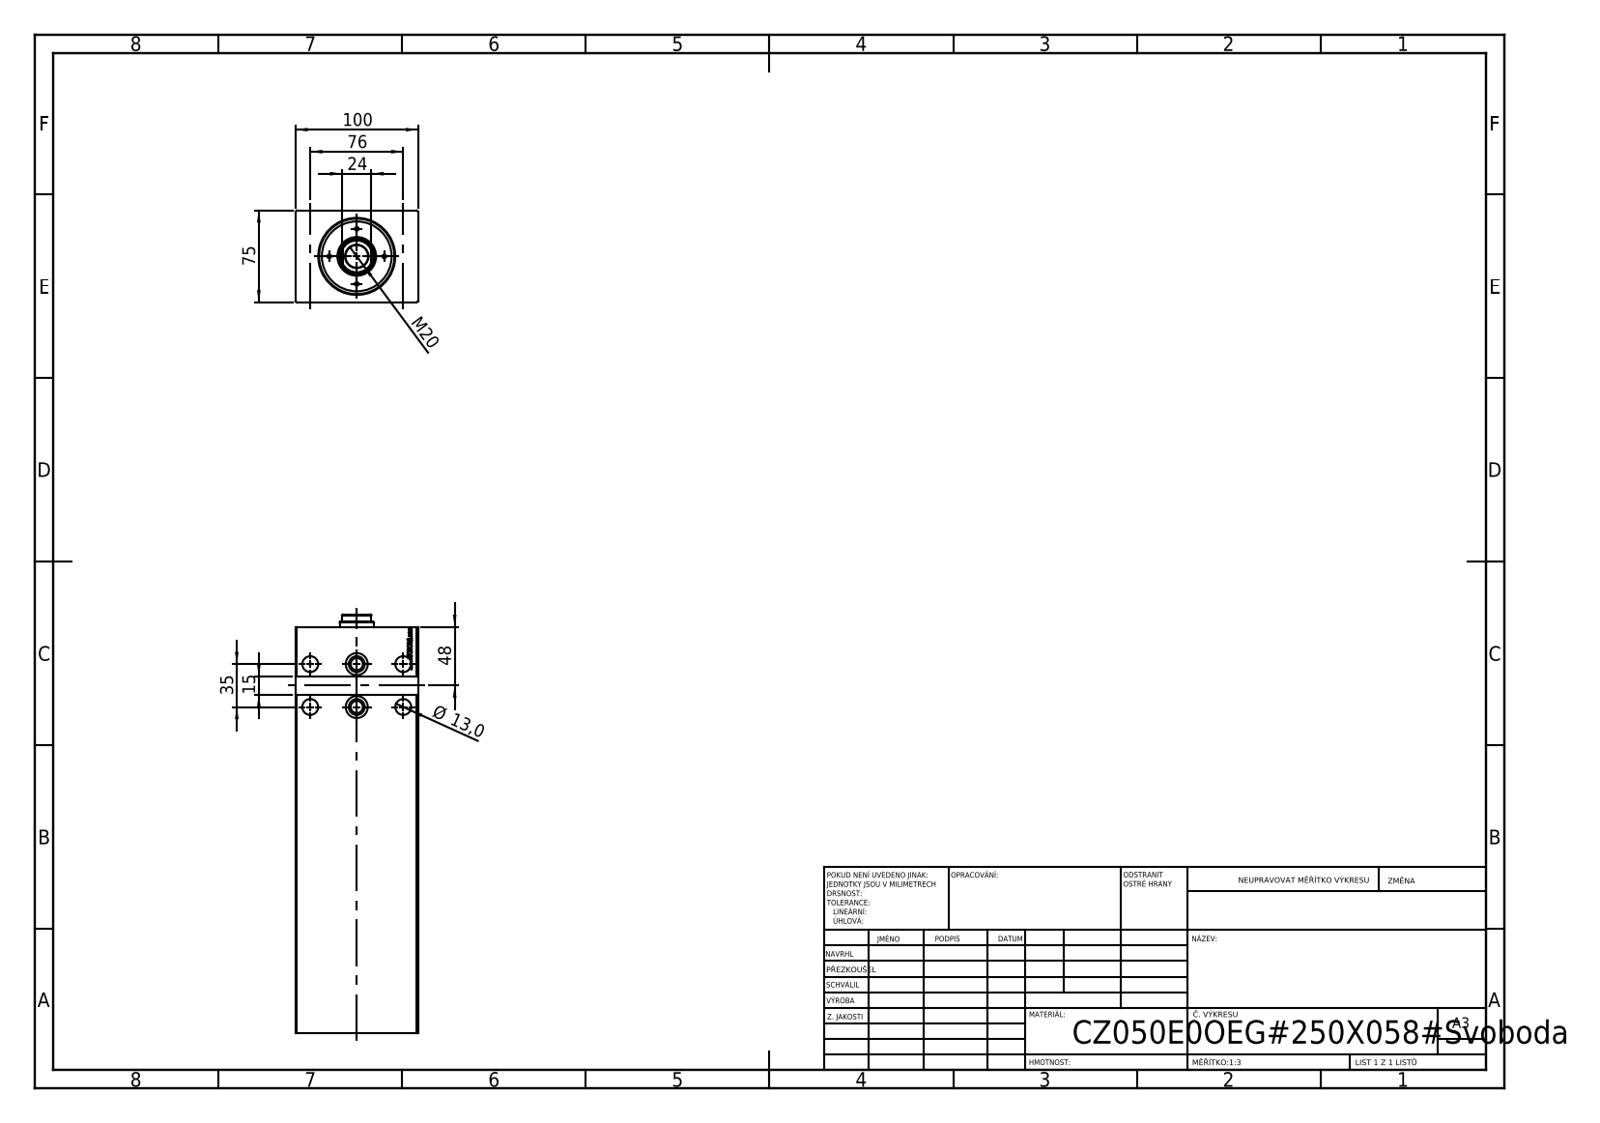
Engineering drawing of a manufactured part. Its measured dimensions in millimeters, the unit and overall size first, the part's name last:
Units: millimetres
Overall size (bounding box): 332 × 100 × 75
Round holes (diameter × count): ⌀13 ×4, ⌀8 ×2, ⌀10 ×2, ⌀18 ×2, ⌀36 ×1, ⌀50 ×1, ⌀61.5 ×1
Round bosses / shafts (diameter × count): ⌀13 ×2
Main face-to-face distances: 75, 100, 332, 314.2, 17.8, 2, 73, 331.8, 17.6, 10
Hole centre spacings: 38, 51.66, 35, 76, 83.67, 19.14, 21.03, 33.71
Volume: 1 818 000 mm³ · Surface area: 192 356 mm²
Bodies: 1 solid, 775 faces (375 planar, 30 cylindrical, 370 other)
STEP written by: SolidWorks 2019 (CONFIG_CONTROL_DESIGN)
